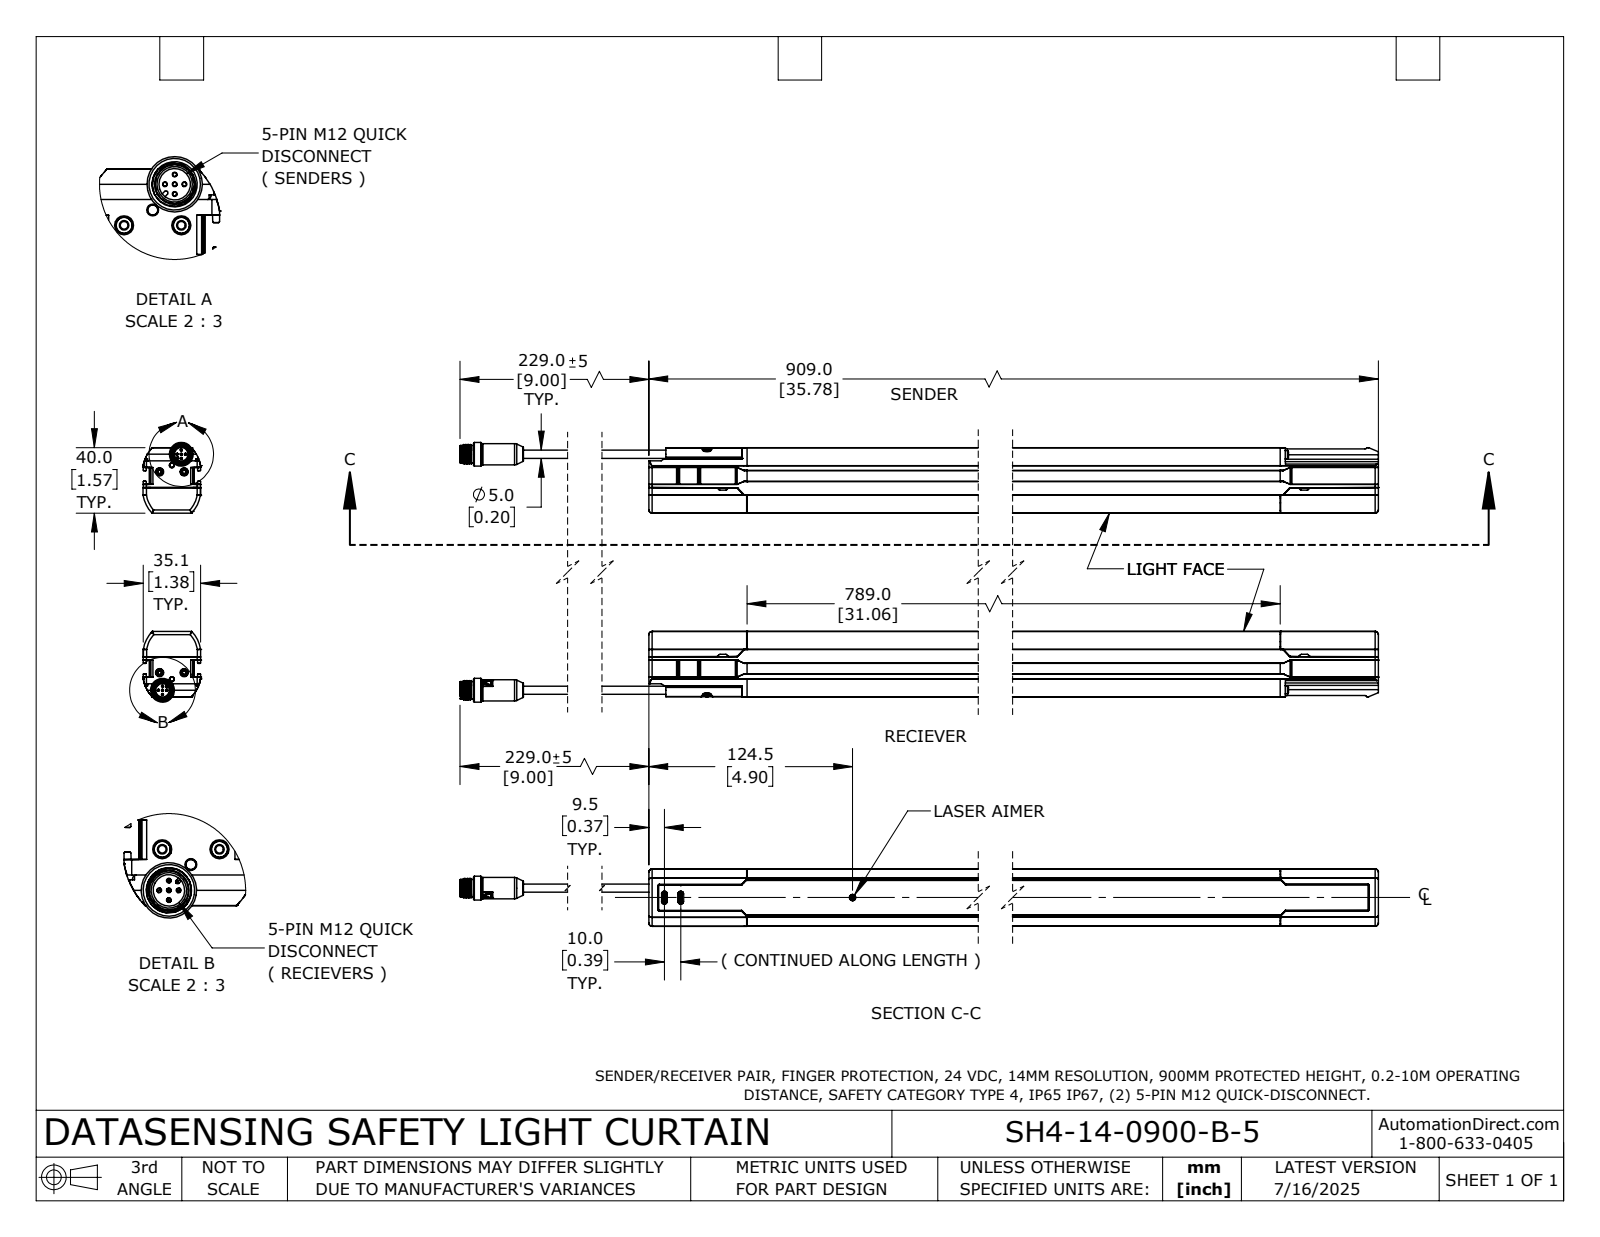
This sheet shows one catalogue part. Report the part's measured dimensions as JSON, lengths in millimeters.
{"part_name": "957920005", "step_written_by": "SolidWorks 2024 (AUTOMOTIVE_DESIGN)", "units": "millimeters", "bodies": {"solids": 4, "faces": 2590, "planar": 1186, "cylindrical": 778, "other": 626}, "overall_size": [1137.3, 158.7, 35.1], "volume_mm3": 2135000, "surface_area_mm2": 381800, "round_holes": [[2, 4], [3, 4], [5, 4], [2.6, 2], [2.6, 2], [2.6, 2], [2.6, 2], [2.8, 2], [8.3, 2], [9.7, 2], [10.3, 2], [10.8, 2]], "round_bosses_or_shafts": [[5, 10], [1, 10], [2.2, 8], [4.4, 4], [14.5, 2], [13, 2], [10.6, 2], [9.5, 2]], "partial_cylinders_radius": [[0.3, 164], [0.4, 66], [0.5, 50], [0.2, 36], [0.8, 20], [0.8, 12], [1.5, 10], [2, 10]], "face_to_face_distances": [38, 114.2, 4, 31, 76.2, 35, 152.2, 27.1, 26.2, 117.7], "hole_center_spacings": [22, 136.6, 138.3, 10.9, 15, 17.1, 122.7, 123.6]}
